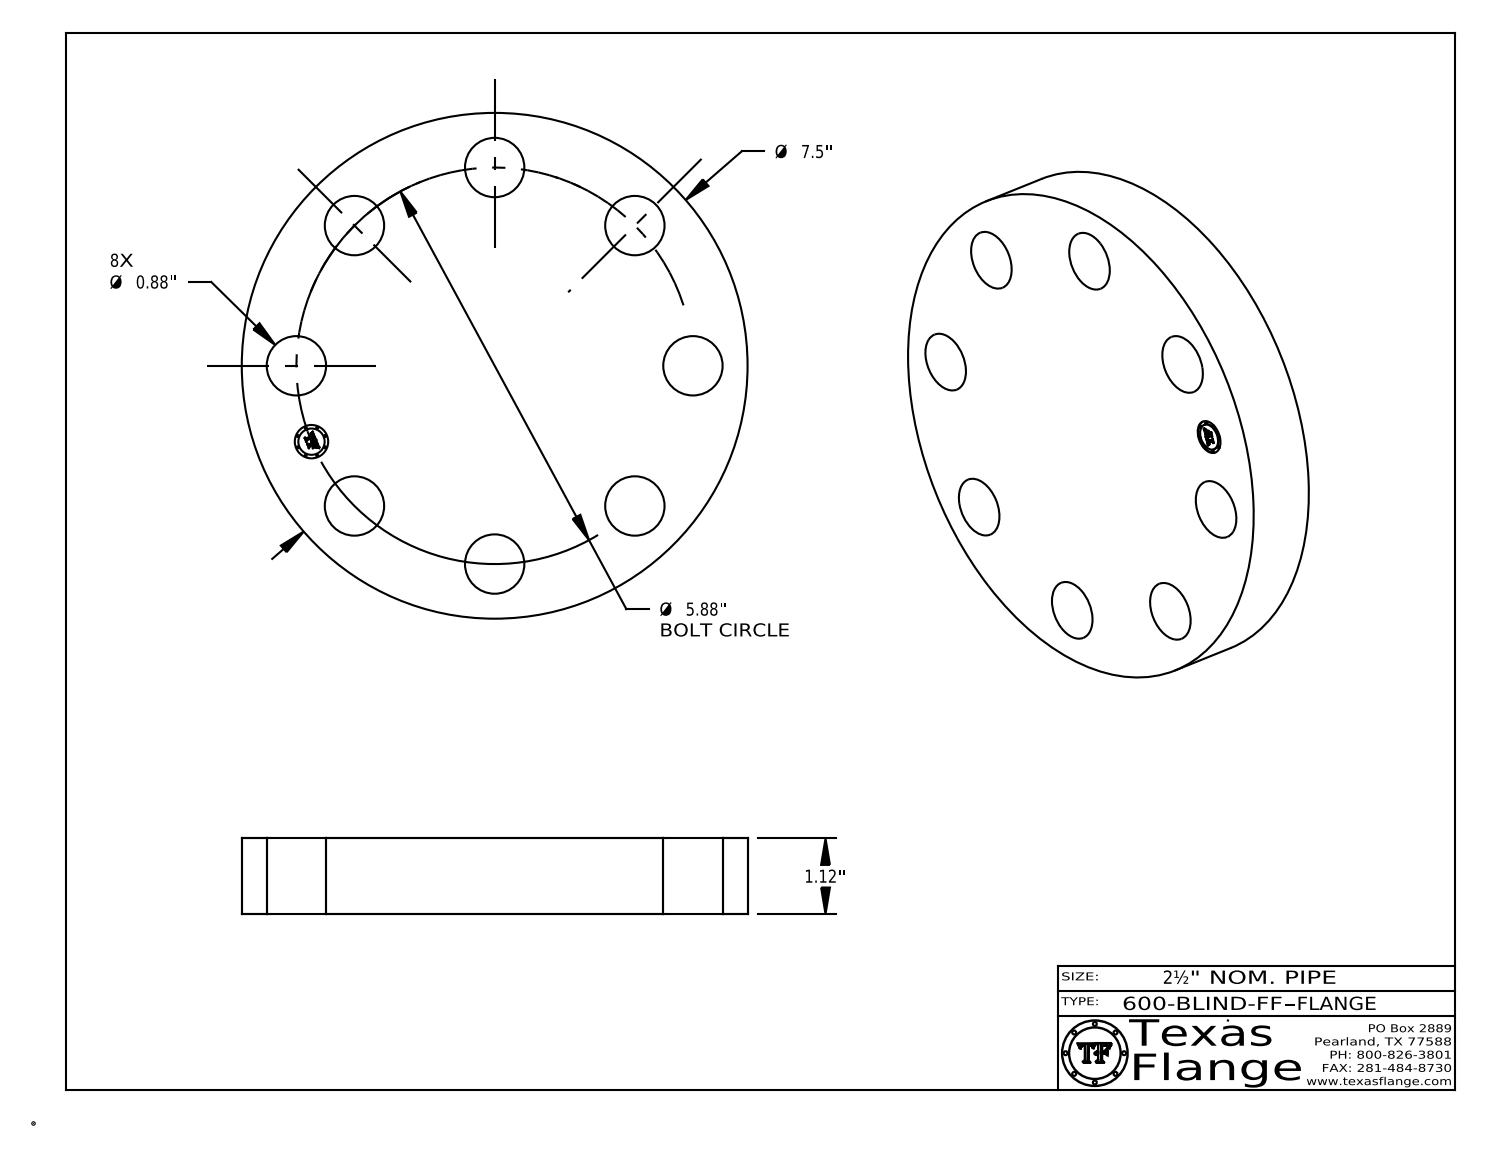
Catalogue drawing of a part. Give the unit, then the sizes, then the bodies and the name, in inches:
Units: inches
Overall size (bounding box): 7.5 × 7.5 × 1.12
Round holes (diameter × count): ⌀0.88 ×8, ⌀0.495 ×1
Round bosses / shafts (diameter × count): ⌀0.03 ×8, ⌀7.5 ×1, ⌀0.39 ×1
Main face-to-face distances: 1.12, 0.015, 1.105, 0.148, 0.145, 0.027, 0.096, 0.123, 0.022, 0.074
Hole centre spacings: 2.25, 5.432, 4.157, 4.158, 3.267, 5.88, 5.88, 1.147
Volume: 44.03 in³ · Surface area: 129.9 in²
Bodies: 1 solid, 405 faces (367 planar, 38 cylindrical, 0 other)
Part name (STEP PRODUCT): 600-BLIND-FF
STEP written by: CATIA V5 STEP AP214 (AUTOMOTIVE_DESIGN)
